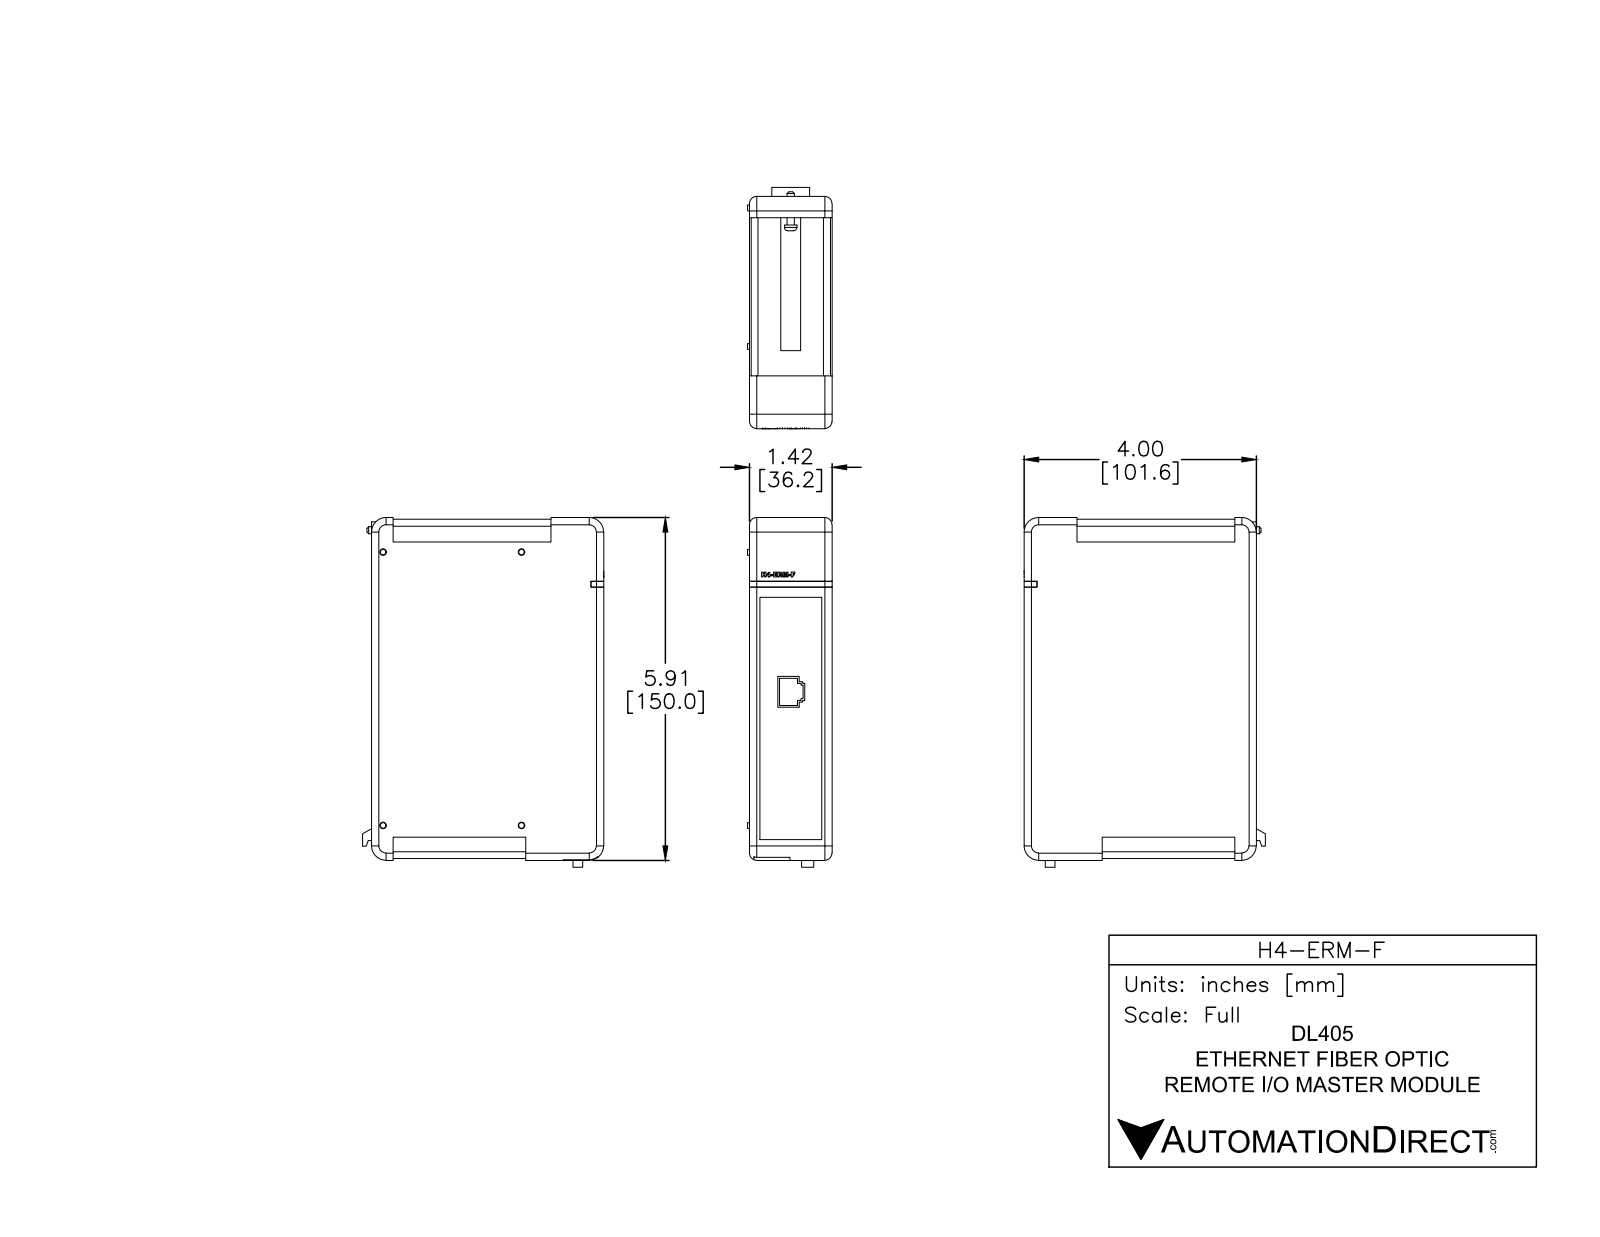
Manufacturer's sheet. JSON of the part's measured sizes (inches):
{"part_name": "H4-ERM-F", "step_written_by": "SolidWorks 2014 (AUTOMOTIVE_DESIGN)", "units": "inches", "bodies": {"solids": 2, "faces": 279, "planar": 210, "cylindrical": 34, "other": 35}, "overall_size": [6.025, 4.156, 1.455], "volume_in3": 32.09, "surface_area_in2": 81.26, "round_bosses_or_shafts": [[0.212, 1], [0.123, 1]], "partial_cylinders_radius": [[0.125, 8], [0.12, 4], [0.25, 4], [0.145, 1], [0.171, 1]], "face_to_face_distances": [1.425, 0.03, 3.97, 1.395, 5.845, 5.875, 4, 0.2, 3.77, 3.8]}
